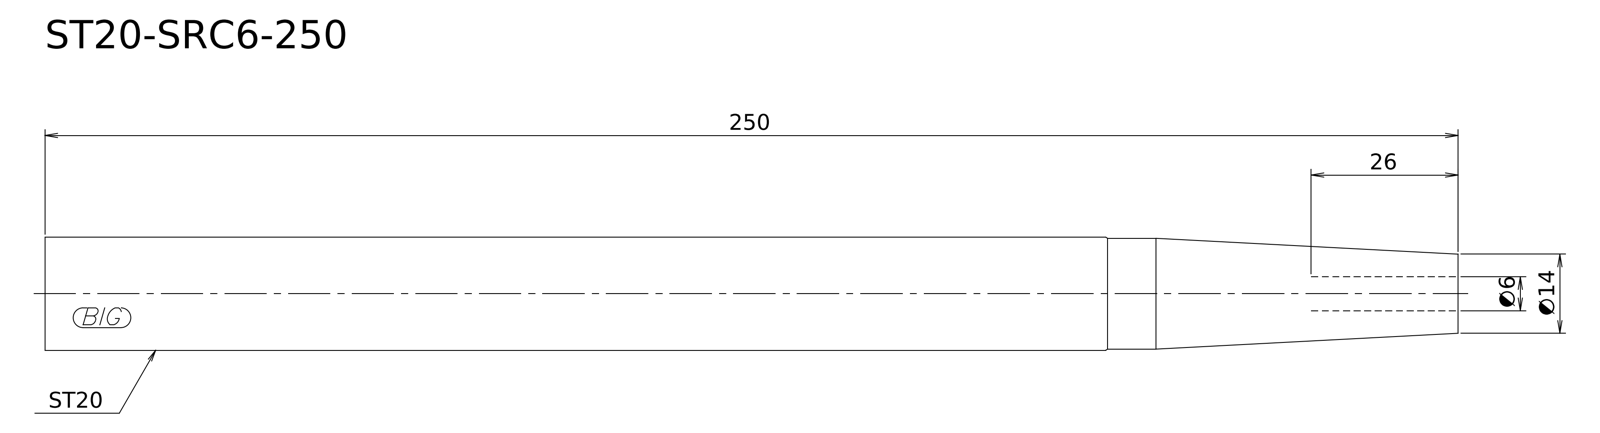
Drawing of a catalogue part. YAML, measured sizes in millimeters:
step_written_by: "Kubotek KeyCreator V8.5.1 (14335) (CONFIG_CONTROL_DESIGN)"
units: millimeters
bodies: {solids: 1, faces: 6, planar: 2, cylindrical: 2, other: 2}
overall_size: [250, 20, 20]
volume: 73599
surface_area: 15635
round_bosses_or_shafts:
  - {diameter: 20, count: 1}
  - {diameter: 19.6, count: 1}
face_to_face_distances: [250]
